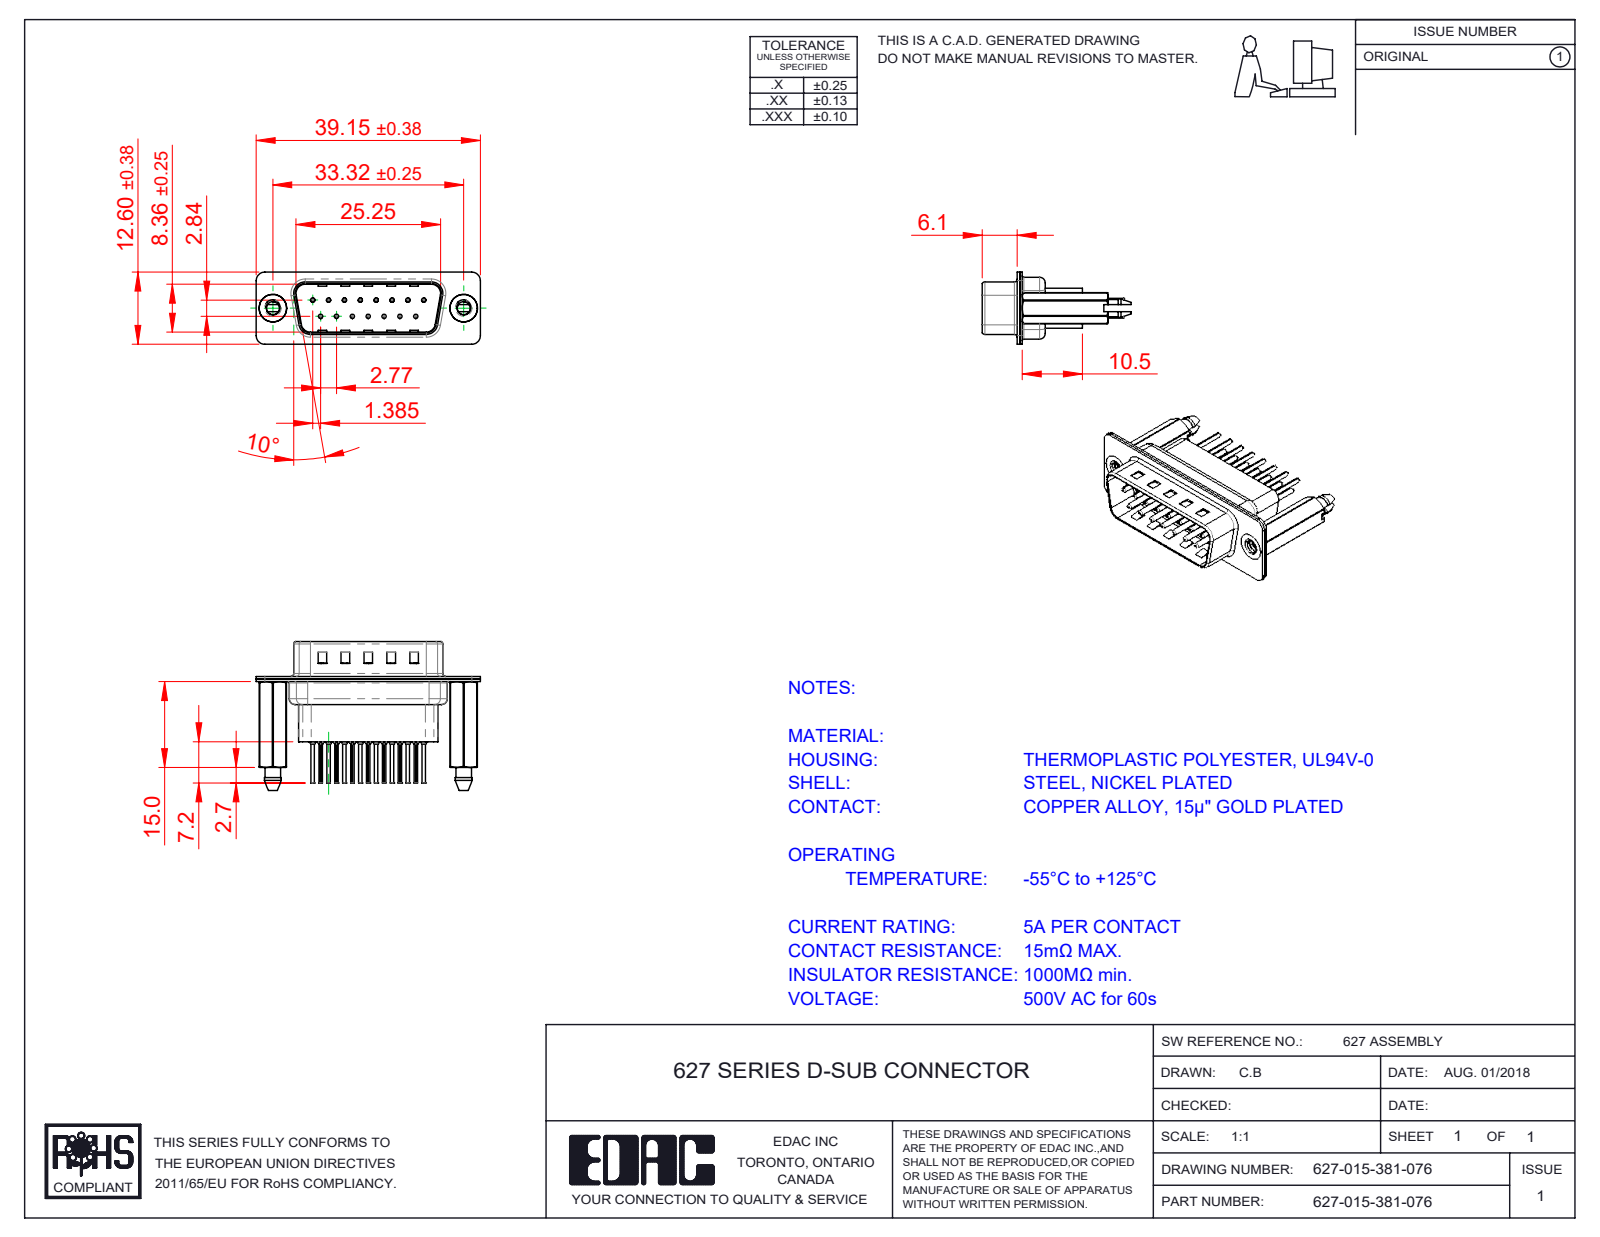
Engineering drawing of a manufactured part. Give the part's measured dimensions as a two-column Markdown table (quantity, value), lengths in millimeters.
| quantity | value |
| --- | --- |
| part name | 627 Contact Row 2_61; 627 Contact Row 1_61; 627 4-40 Threaded Boardlock_HP81; 627 Shell Rear_15 Contacts (+3 more) |
| STEP written by | SolidWorks 2020 (CONFIG_CONTROL_DESIGN) |
| units | millimeters |
| bodies | 20 solids, 1918 faces (531 planar, 754 cylindrical, 633 other) |
| overall size | 39.15 × 25.9 × 12.6 |
| volume | 2 936 mm³ |
| surface area | 7 555 mm² |
| round holes (diameter × count) | 0.2 × 15, 0.35 × 15, 1.1 × 15, 1.6 × 15, 2.26 × 2, 4 × 2, 4.8 × 2 |
| round bosses / shafts (diameter × count) | 2 × 15, 1.5 × 15, 0.75 × 15, 0.6 × 15, 4.9 × 2 |
| partial cylindrical surfaces (radius × count) | 0.1 × 30, 1.5 × 18, 2 × 12, 1.6 × 10, 0.5 × 8, 0.25 × 4, 0.6 × 4, 0.65 × 4 |
| main face-to-face distances | 0.4, 0.45, 0.9, 0.82, 9.58, 4.76, 1.5, 0.68, 7.68, 1.4 |
| hole center spacings | 3.16, 2.77, 5.54, 8.31, 11.08, 5.03, 5.04, 7.48 |
